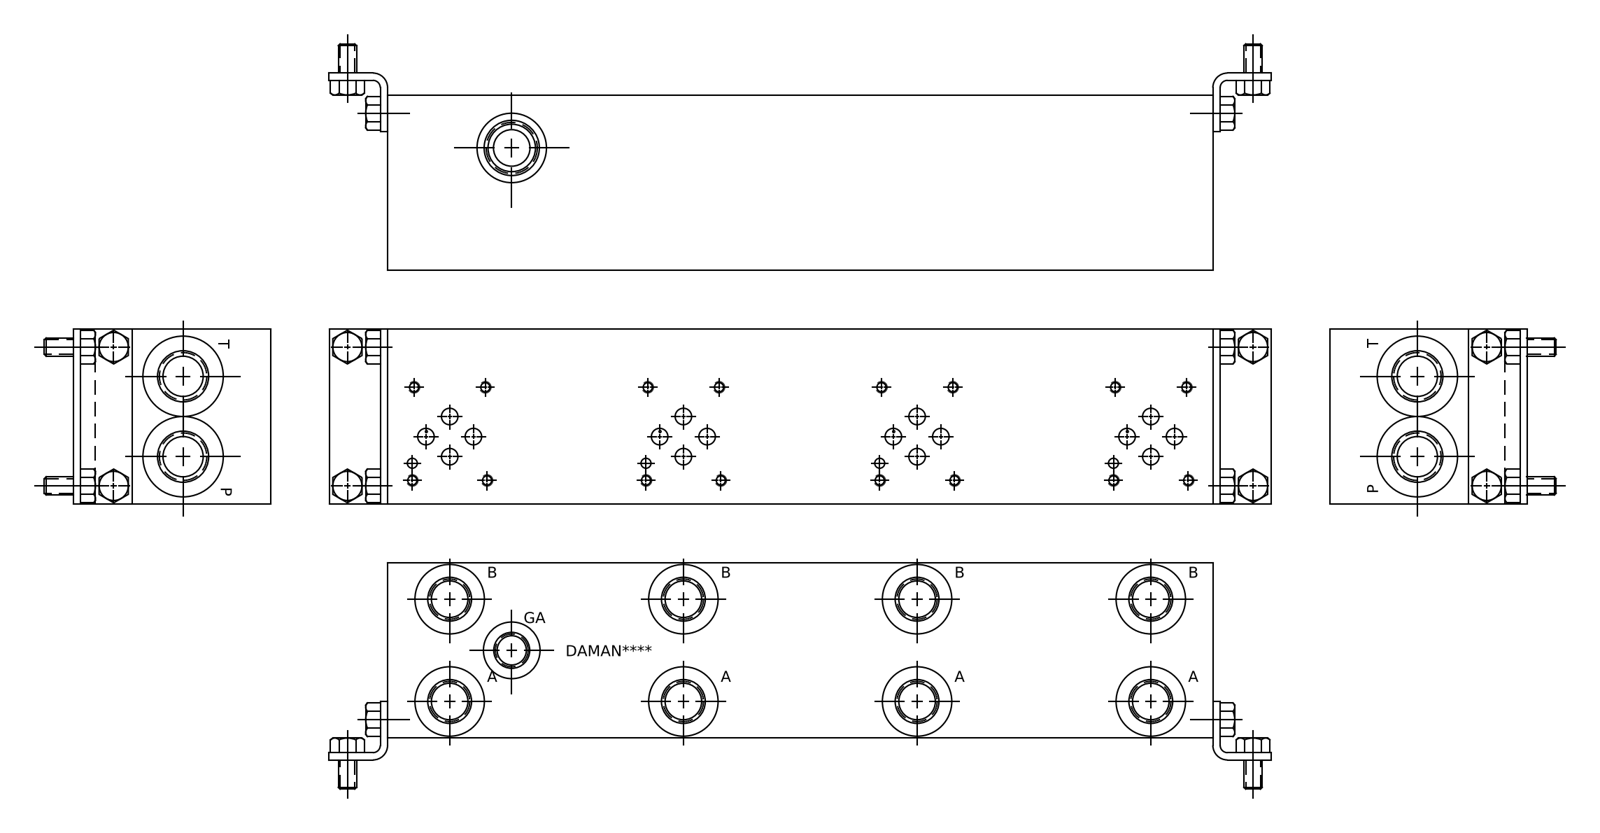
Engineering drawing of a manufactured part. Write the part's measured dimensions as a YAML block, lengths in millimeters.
part_name: "Part_AD03P044S~C_3D"
step_written_by: "Autodesk Inventor 2021 (AUTOMOTIVE_DESIGN)"
units: millimeters
bodies: {solids: 1, faces: 883, planar: 452, cylindrical: 141, other: 290}
overall_size: [358.77, 76.2, 76.2]
volume: 1956000
surface_area: 150784
round_holes:
  - {diameter: 3.78, count: 16}
  - {diameter: 4.83, count: 16}
  - {diameter: 7.14, count: 12}
  - {diameter: 17.5, count: 9}
  - {diameter: 19.05, count: 9}
  - {diameter: 19.25, count: 9}
  - {diameter: 14.3, count: 8}
  - {diameter: 30.63, count: 8}
  - {diameter: 3.96, count: 4}
  - {diameter: 6.35, count: 4}
  - {diameter: 15.88, count: 3}
  - {diameter: 6.53, count: 2}
partial_cylinders:
  - {radius: 5.25, count: 1}
  - {radius: 6.15, count: 1}
face_to_face_distances: [76.2, 0.79, 358.77, 75.41, 0.78, 357.98, 357.99, 357.2, 61.14, 15.06]
hole_center_spacings: [101.6, 203.2, 304.8, 91.68, 91.71, 103.09, 110.9, 112.25]
